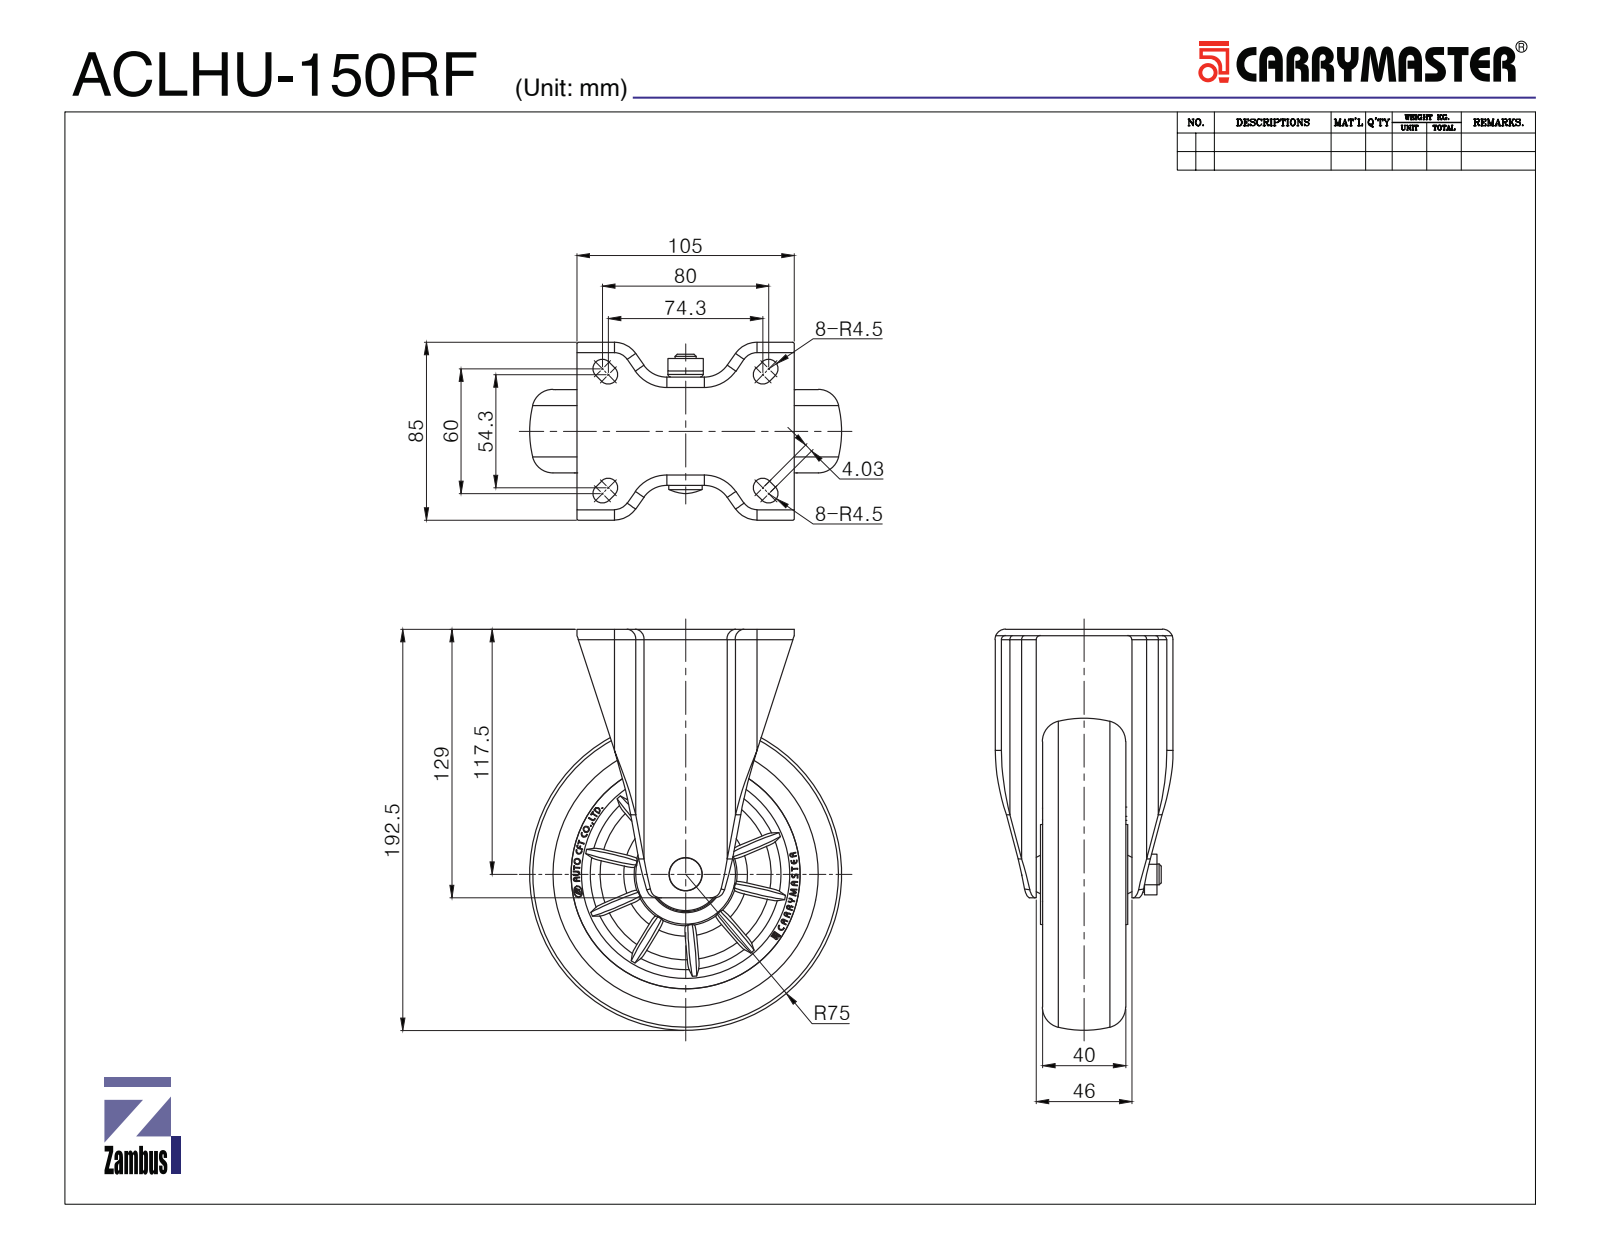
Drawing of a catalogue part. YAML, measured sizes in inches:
part_name: "ACLMU-150RF"
step_written_by: "SolidWorks 2015 (CONFIG_CONTROL_DESIGN)"
units: inches
bodies: {solids: 7, faces: 1316, planar: 709, cylindrical: 197, other: 410}
overall_size: [7.589, 5.906, 3.365]
volume: 40.18
surface_area: 286
round_holes:
  - {diameter: 0.067, count: 2}
  - {diameter: 0.335, count: 1}
  - {diameter: 0.394, count: 1}
  - {diameter: 0.472, count: 1}
  - {diameter: 1.181, count: 1}
  - {diameter: 1.26, count: 1}
  - {diameter: 4.331, count: 1}
round_bosses_or_shafts:
  - {diameter: 0.026, count: 2}
  - {diameter: 5.118, count: 1}
  - {diameter: 1.378, count: 1}
  - {diameter: 0.669, count: 1}
partial_cylinders:
  - {radius: 0.039, count: 44}
  - {radius: 0.866, count: 20}
  - {radius: 0.079, count: 8}
  - {radius: 0.177, count: 8}
  - {radius: 0.197, count: 8}
  - {radius: 0.374, count: 4}
  - {radius: 0.492, count: 4}
  - {radius: 0.531, count: 4}
face_to_face_distances: [0.118, 0.236, 0.906, 1.811, 1.575, 0.197, 1.614, 0.709, 1.693, 1.929]
hole_center_spacings: [1.567, 2.098, 2.098]
